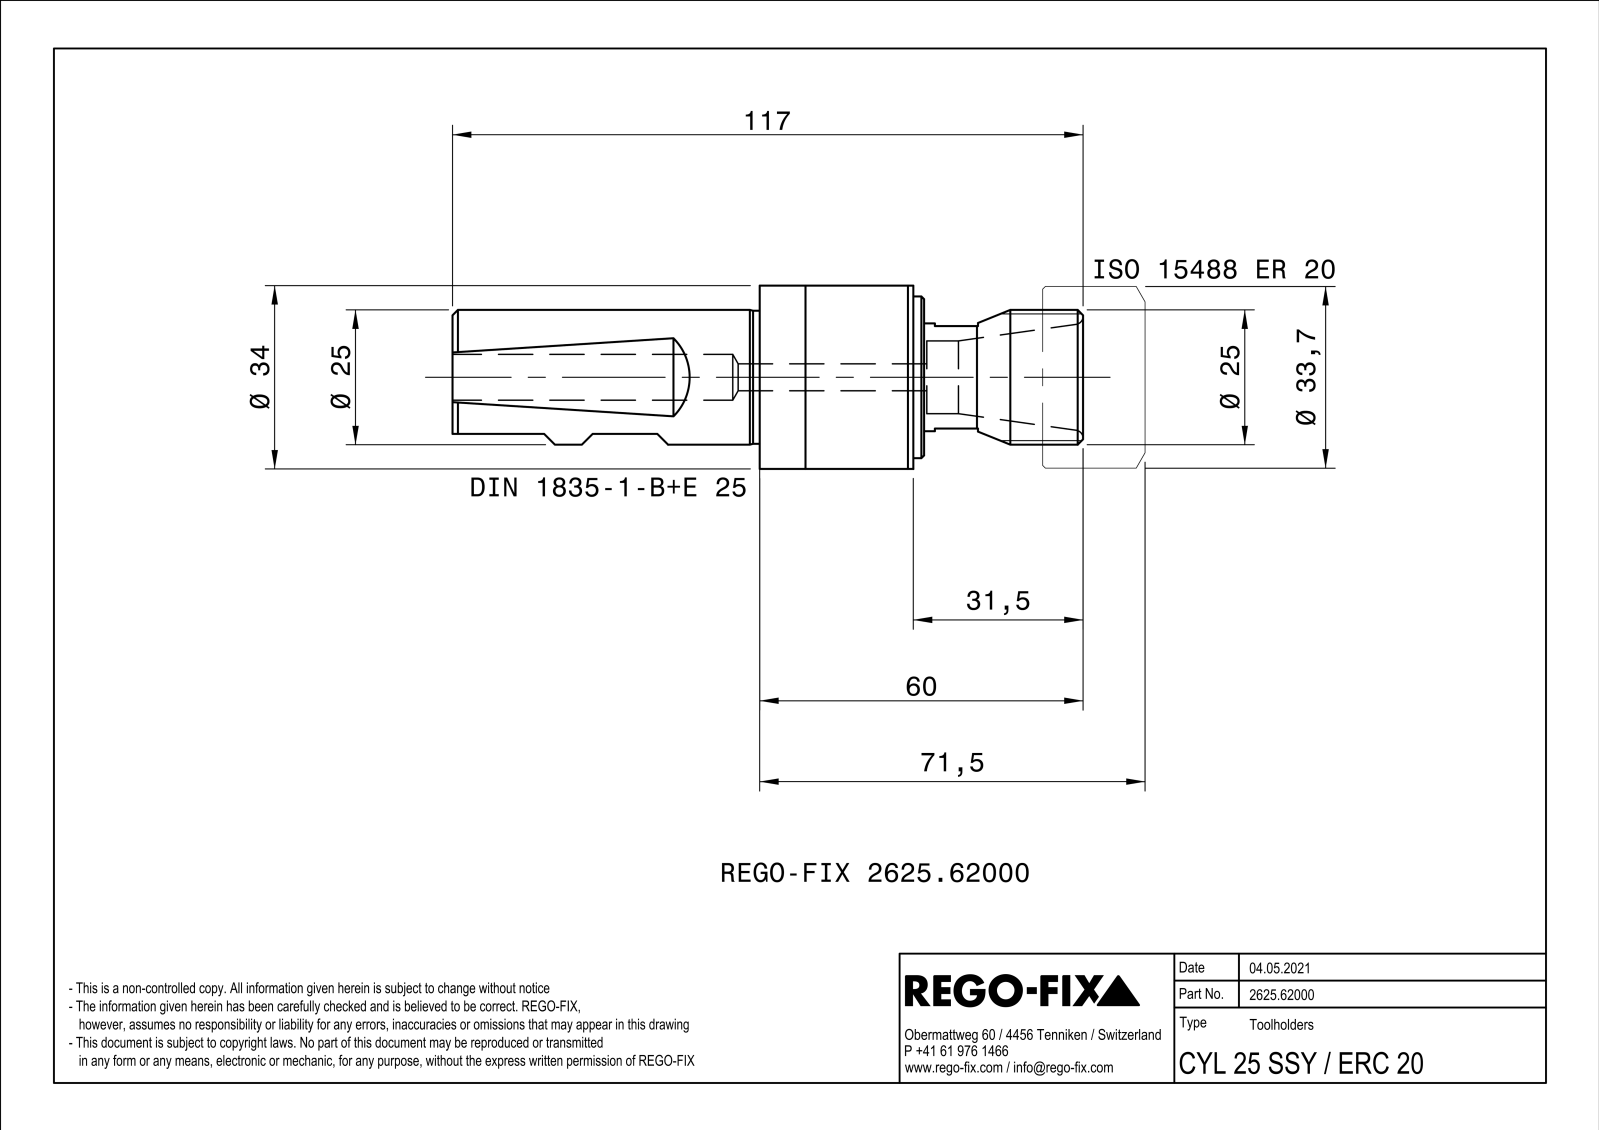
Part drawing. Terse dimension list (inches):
name: NOCUT
written by: SIEMENS PLM Software Solid Edge ST10 (AUTOMOTIVE_DESIGN)
unit: in
bodies: 8 solids, 90 faces (30 planar, 25 cylindrical, 35 other)
size: 4.606 × 1.339 × 1.339
volume: 3.389 in³; area: 23.82 in²
holes: 1× ⌀0.197, 1× ⌀0.248, 1× ⌀0.335, 1× ⌀0.531, 1× ⌀0.9
bosses: 1× ⌀1.339, 1× ⌀1.181, 1× ⌀1.142, 1× ⌀1.024, 1× ⌀0.984, 1× ⌀0.966, 1× ⌀0.787, 1× ⌀0.764
rounds: 1× R0.063
face distances: 2.244, 1.201, 3.445, 0.118, 1.083, 3.327, 0.02, 0.138, 1.22, 3.465
